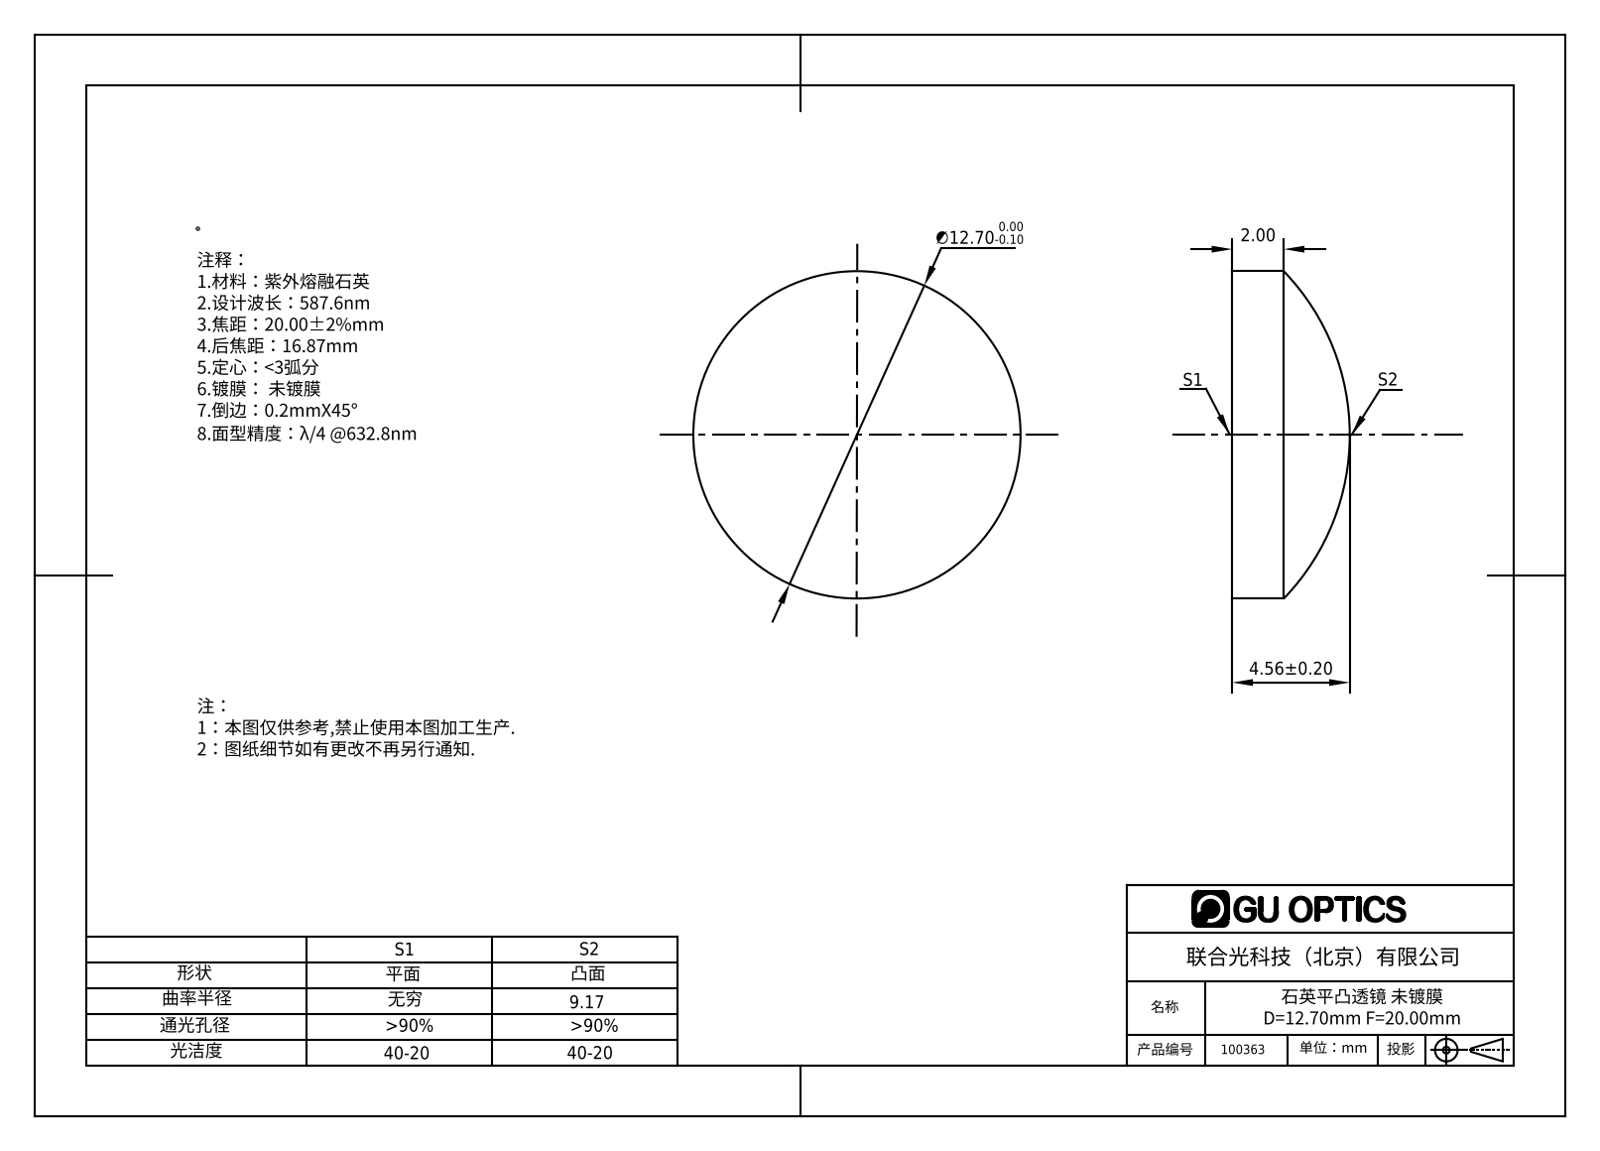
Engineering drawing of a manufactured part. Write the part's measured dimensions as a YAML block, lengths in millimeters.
part_name: "100363"
step_written_by: "SolidWorks 2016 (AUTOMOTIVE_DESIGN)"
units: millimeters
bodies: {solids: 1, faces: 5, planar: 1, cylindrical: 2, other: 2}
overall_size: [12.7, 12.7, 4.56]
volume: 424
surface_area: 354
round_bosses_or_shafts:
  - {diameter: 12.7, count: 1}
